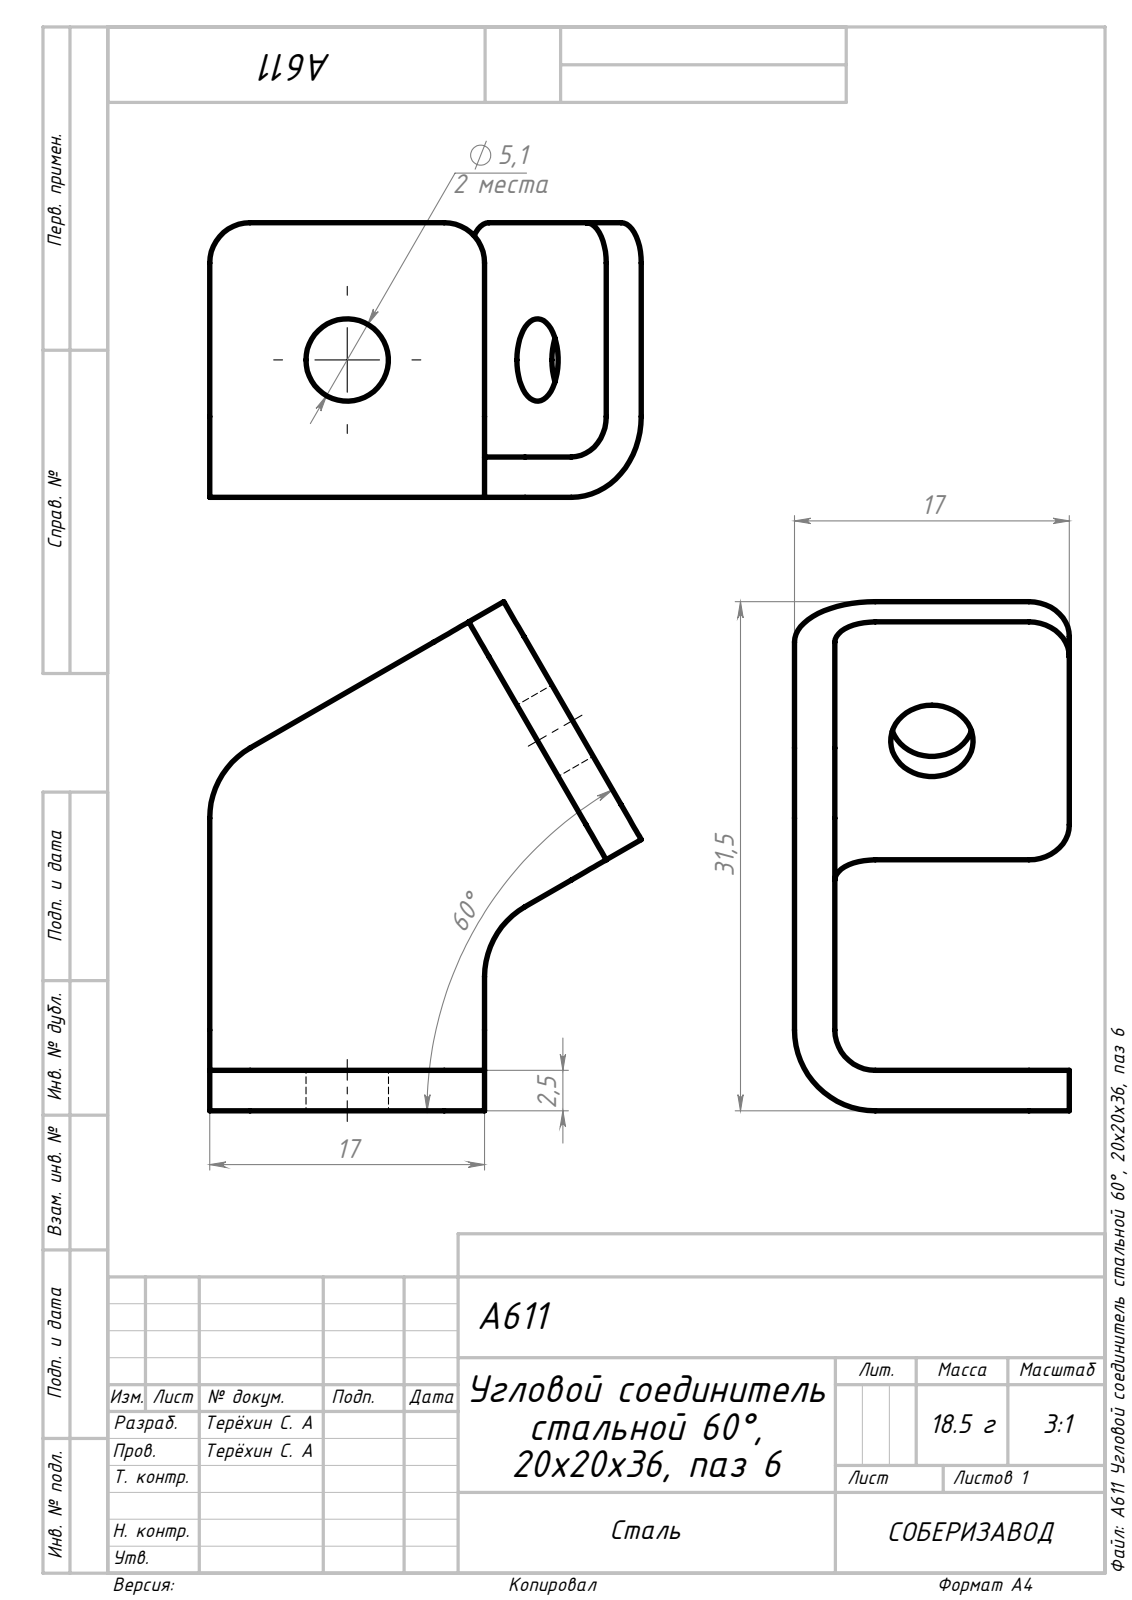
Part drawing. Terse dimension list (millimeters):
written by: SolidWorks 2021 (AUTOMOTIVE_DESIGN)
unit: mm
bodies: 1 solid, 34 faces (20 planar, 14 cylindrical, 0 other)
size: 31.5 × 26.69 × 17
volume: 2 348 mm³; area: 2 320 mm²
holes: 2× ⌀5.1
rounds: 6× R2.5, 4× R5
face distances: 2.5, 17, 14.5
